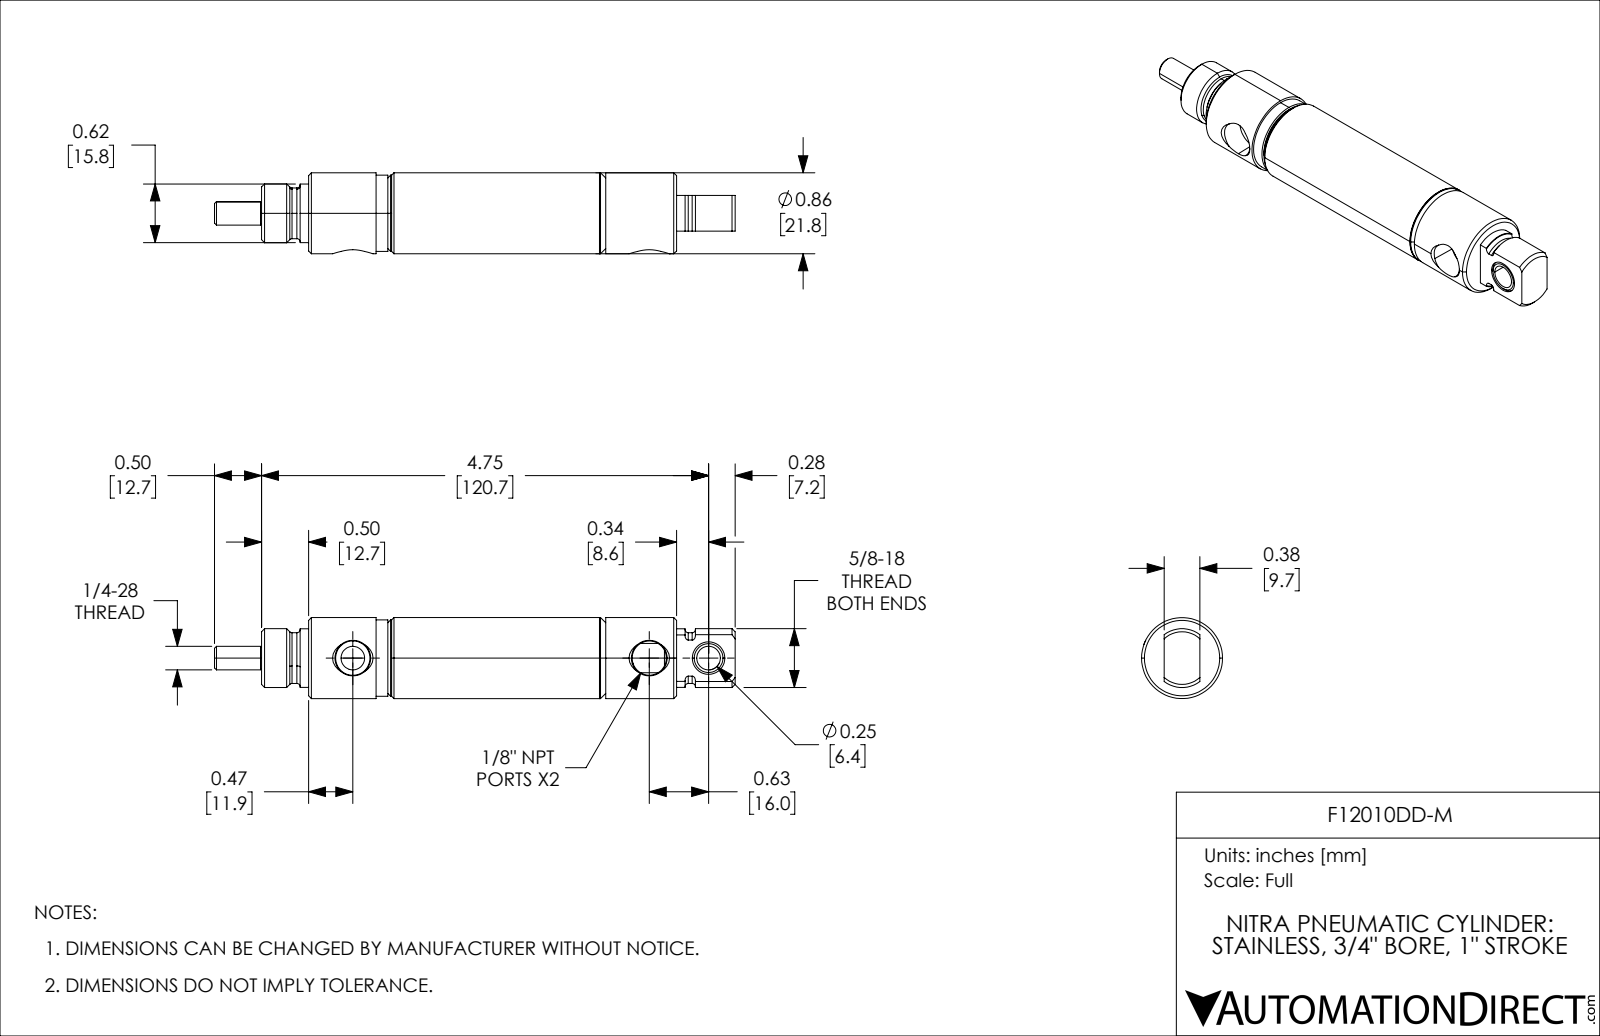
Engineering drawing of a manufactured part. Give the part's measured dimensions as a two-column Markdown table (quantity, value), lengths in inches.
| quantity | value |
| --- | --- |
| part name | F12010DD-M_9; F12010DD-M_5; F12010DD-M; F12010DD-M_7 (+2 more) |
| STEP written by | SolidWorks 2021 (CONFIG_CONTROL_DESIGN) |
| units | inches |
| bodies | 5 solids, 158 faces (29 planar, 61 cylindrical, 68 other) |
| overall size | 5.532 × 0.86 × 0.86 |
| volume | 1.961 in³ |
| surface area | 31.36 in² |
| round holes (diameter × count) | 0.25 × 1, 0.251 × 1, 0.274 × 1, 0.312 × 1, 0.346 × 1, 0.363 × 1, 0.5 × 1, 0.702 × 1 |
| round bosses / shafts (diameter × count) | 0.86 × 1, 0.81 × 1, 0.762 × 1, 0.625 × 1, 0.622 × 1, 0.539 × 1, 0.25 × 1, 0.23 × 1 |
| partial cylindrical surfaces (radius × count) | 0.269 × 1 |
| main face-to-face distances | 0.844, 1.594, 3.438, 1, 1.844, 2.816, 1.816, 0.972, 2.094, 0.5 |
| hole center spacings | 0.63, 3.15, 3.78 |
